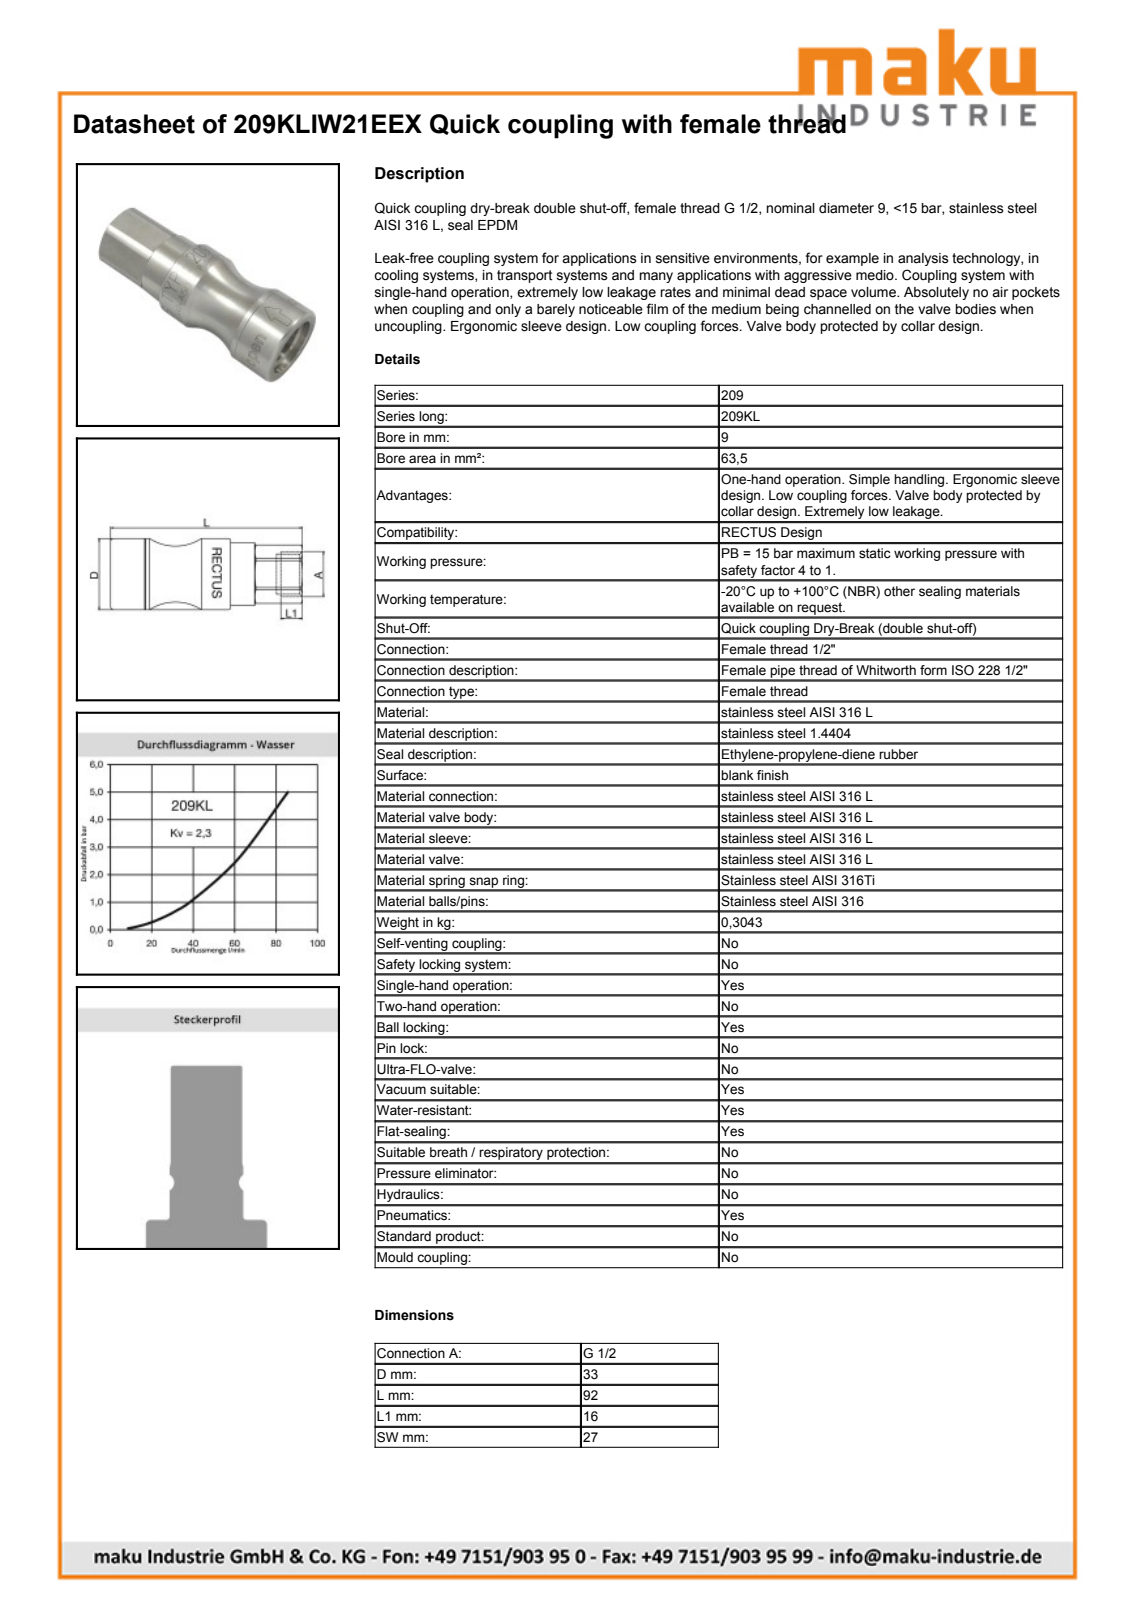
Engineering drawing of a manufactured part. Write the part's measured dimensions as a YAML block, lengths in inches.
part_name: "D108680"
step_written_by: "Autodesk Inventor 2013 (AUTOMOTIVE_DESIGN)"
units: inches
bodies: {solids: 1, faces: 1037, planar: 380, cylindrical: 127, other: 530}
overall_size: [3.63, 1.299, 1.299]
volume: 3.427
surface_area: 29.18
round_holes:
  - {diameter: 0.733, count: 1}
  - {diameter: 0.984, count: 1}
  - {diameter: 1.006, count: 1}
  - {diameter: 1.055, count: 1}
  - {diameter: 1.079, count: 1}
  - {diameter: 1.083, count: 1}
  - {diameter: 1.15, count: 1}
  - {diameter: 1.201, count: 1}
  - {diameter: 1.236, count: 1}
round_bosses_or_shafts:
  - {diameter: 1.299, count: 1}
  - {diameter: 1.181, count: 1}
  - {diameter: 1.142, count: 1}
  - {diameter: 1.059, count: 1}
  - {diameter: 0.973, count: 1}
partial_cylinders:
  - {radius: 0.646, count: 1}
face_to_face_distances: [1.063, 3.078, 1.064, 3.63, 0.552, 0.059, 2.079, 1, 1.551, 0.441]
